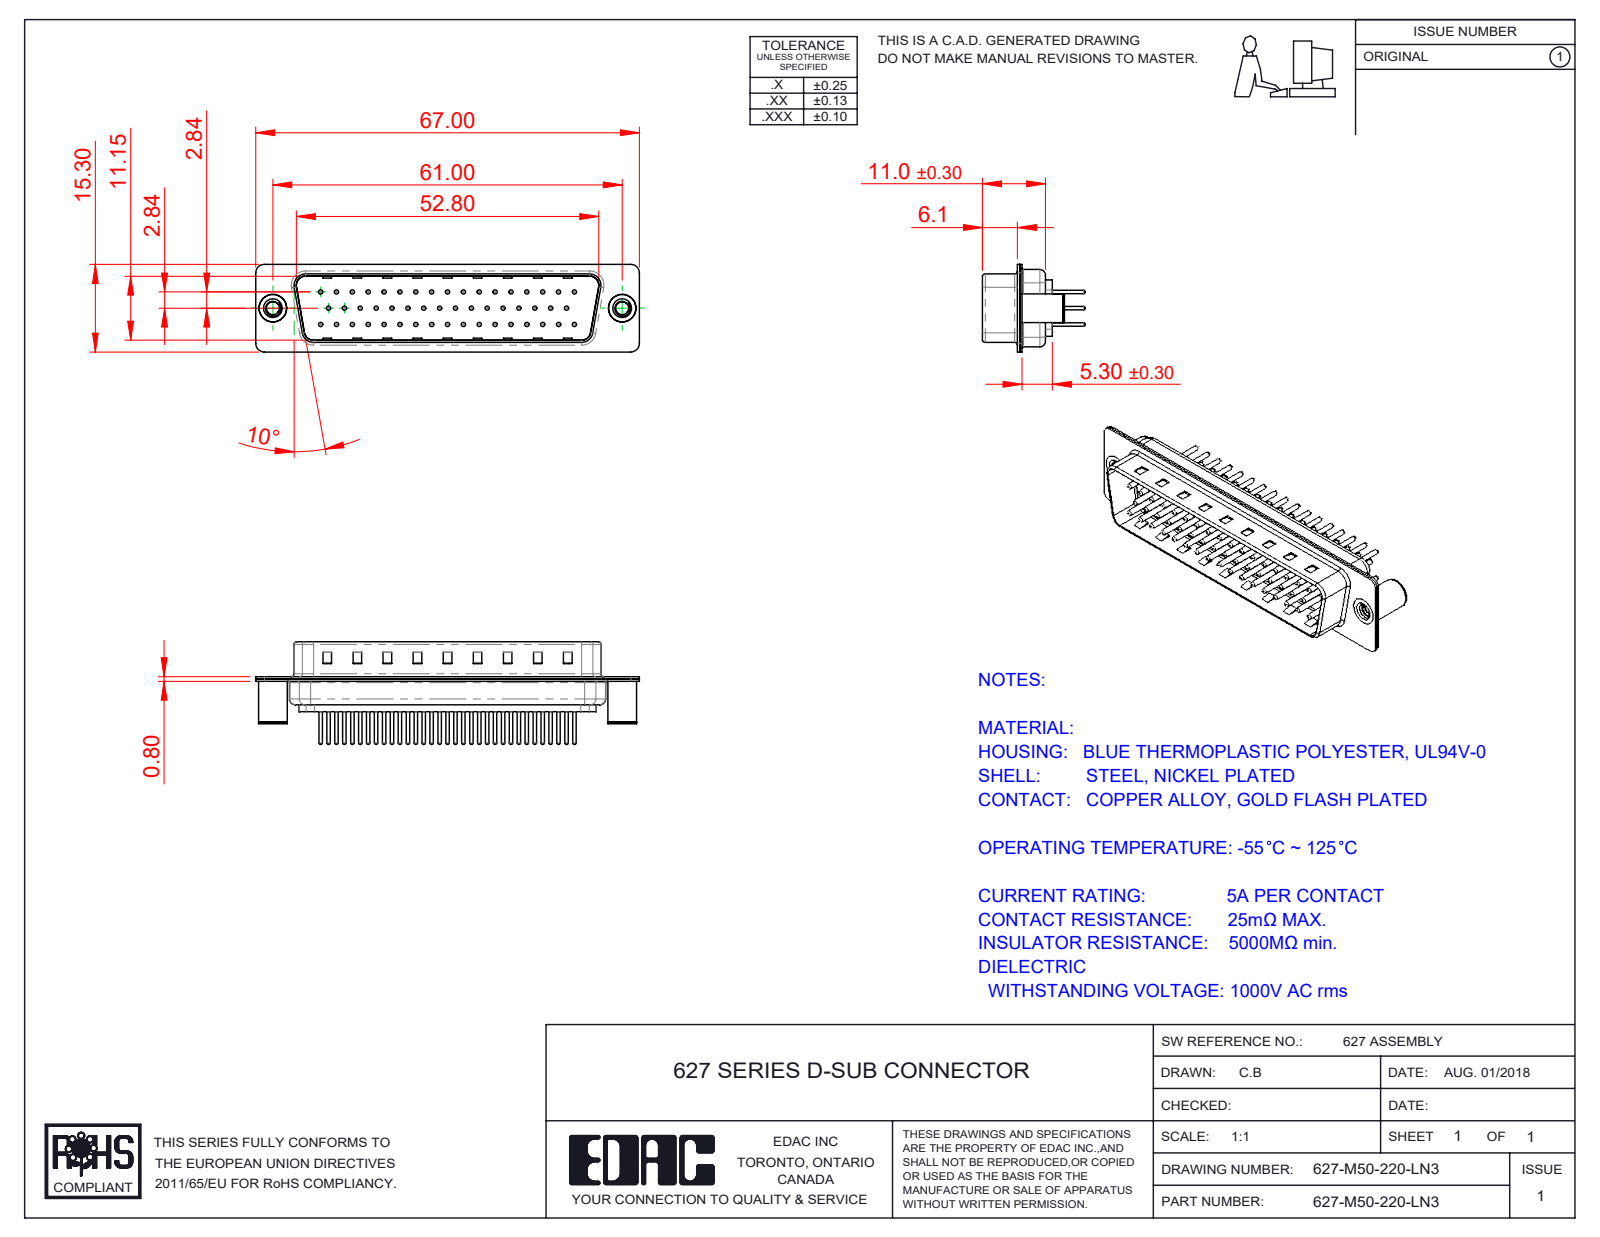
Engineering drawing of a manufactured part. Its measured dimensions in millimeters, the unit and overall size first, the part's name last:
Units: millimetres
Overall size (bounding box): 67 × 17.9 × 15.3
Round holes (diameter × count): ⌀0.75 ×50, ⌀1.6 ×50, ⌀2 ×50, ⌀2.26 ×2, ⌀3.26 ×2, ⌀4 ×2, ⌀4.8 ×2
Round bosses / shafts (diameter × count): ⌀1.5 ×50, ⌀0.6 ×50, ⌀5 ×2, ⌀4.9 ×2
Partial cylindrical surfaces — rounded edges, fillets, slot ends (radius × count): R1.5 ×16, R2 ×12, R0.5 ×8, R1.6 ×8, R0.25 ×4, R0.6 ×4, R0.65 ×4, R0.9 ×4
Main face-to-face distances: 0.4, 11.55, 5.7, 6.1, 0.78, 0.77, 12.33, 5.3, 12.32, 13.1
Hole centre spacings: 3.16, 2.77, 5.54, 8.31, 11.08, 13.85, 16.62, 5.03
Volume: 4 648 mm³ · Surface area: 10 957 mm²
Bodies: 55 solids, 2296 faces (553 planar, 865 cylindrical, 878 other)
Part name (STEP PRODUCT): 627M Shell Front_50 Contacts; 627M Contact Row 3_20; 627M Contact Row 2_20; 627-M50-220-LN3 (+4 more)
STEP written by: SolidWorks 2020 (CONFIG_CONTROL_DESIGN)
